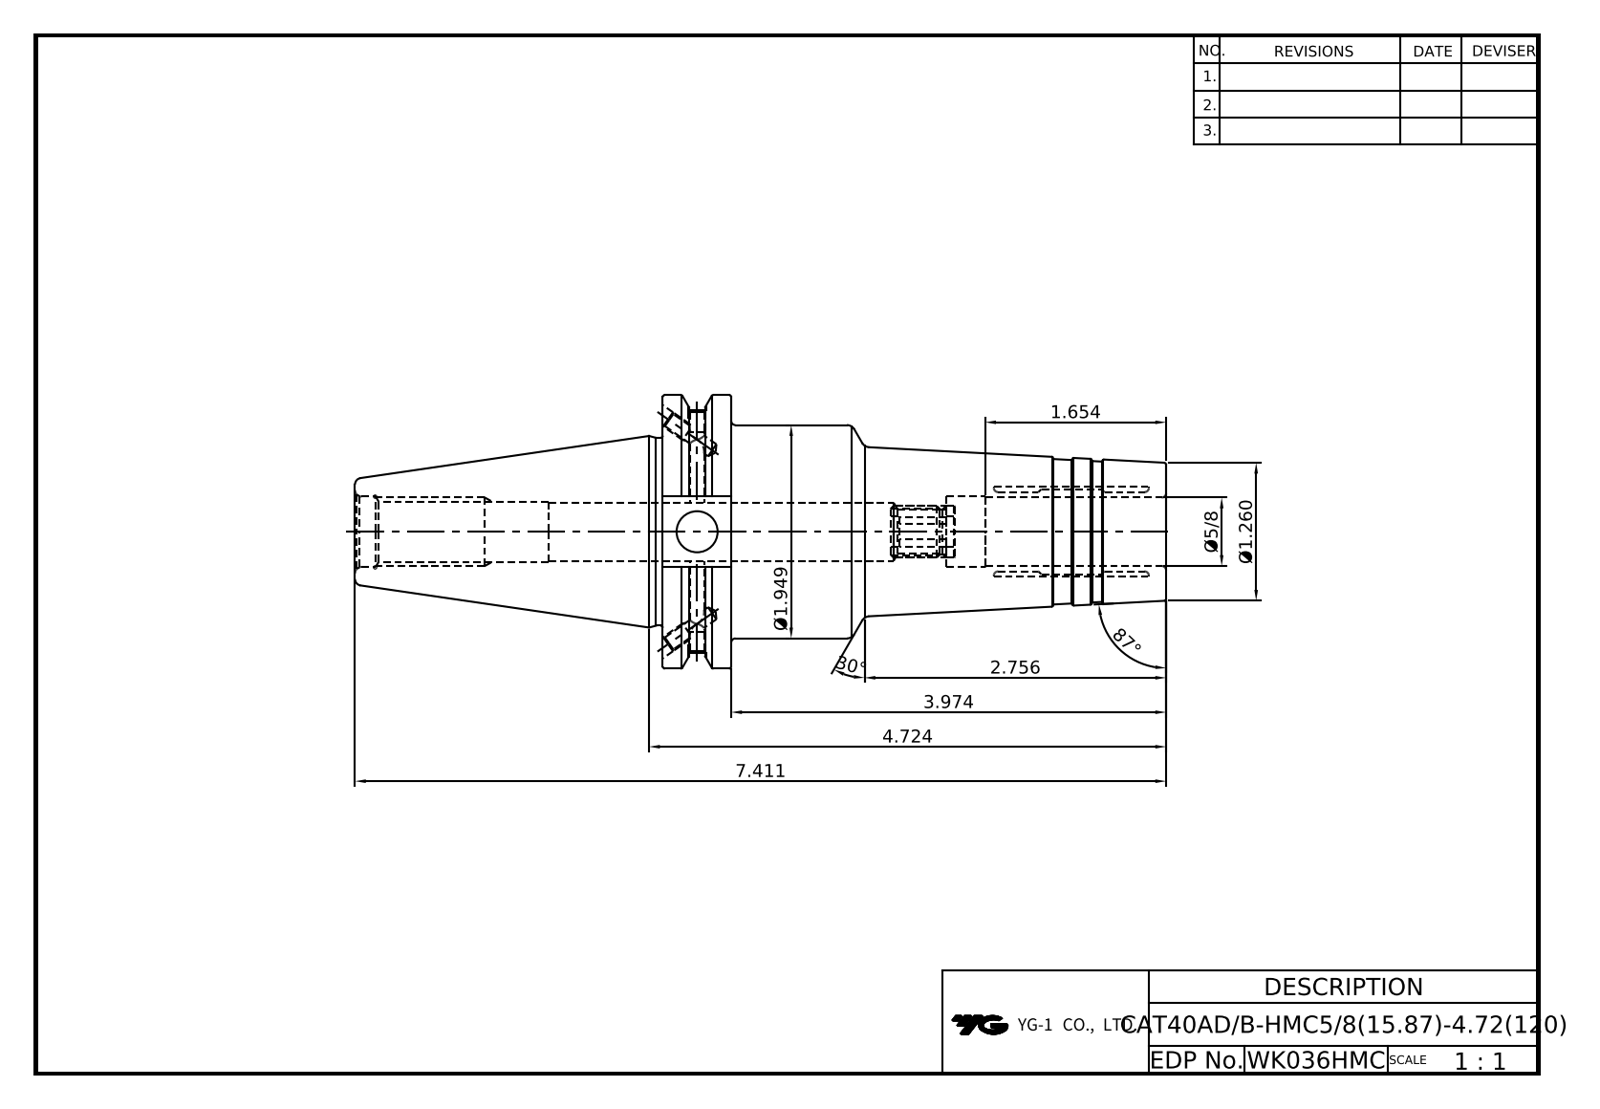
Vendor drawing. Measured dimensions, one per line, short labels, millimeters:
name: LO-CAT40ADB-HMC15.875-120
written by: Autodesk Inventor 2020 (AUTOMOTIVE_DESIGN)
unit: mm
bodies: 1 solid, 106 faces (36 planar, 30 cylindrical, 40 other)
size: 188.25 × 63.5 × 61.09
volume: 212 595 mm³; area: 37 161 mm²
holes: 4× ⌀3.24, 2× ⌀4, 2× ⌀4.2, 1× ⌀9.53, 1× ⌀10.92, 1× ⌀13, 1× ⌀13.39, 1× ⌀15.88, 1× ⌀16.3, 1× ⌀16.4
bosses: 1× ⌀63.5, 1× ⌀49.5, 1× ⌀43.6
rounds: 1× R8.19, 1× R28.15
face distances: 15.88, 116.83, 100.95, 47.6, 16.38, 71.42, 87.3, 188.25, 137.25, 65.83
